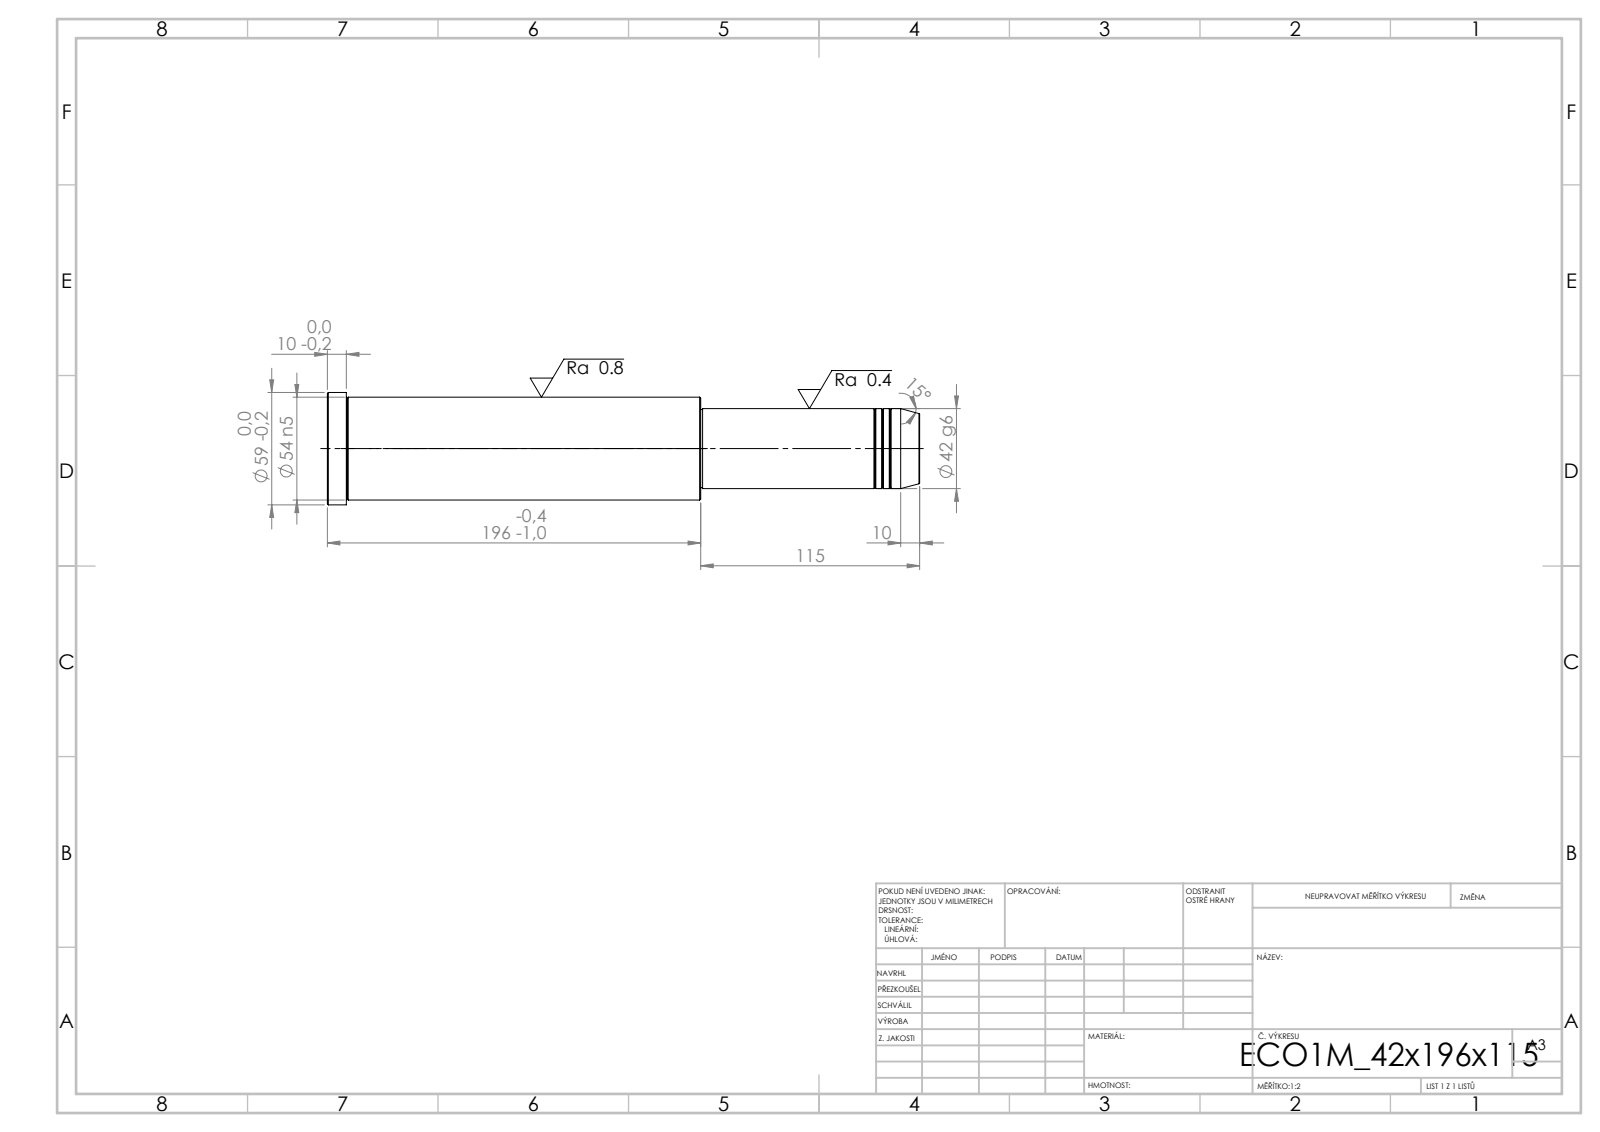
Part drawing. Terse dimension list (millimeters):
written by: SolidWorks 2019 (CONFIG_CONTROL_DESIGN)
unit: mm
bodies: 1 solid, 43 faces (5 planar, 14 cylindrical, 24 other)
size: 311 × 59 × 59
volume: 610 622 mm³; area: 53 998 mm²
bosses: 1× ⌀59, 1× ⌀54, 1× ⌀42, 1× ⌀41
face distances: 311, 115, 196, 301, 186, 10, 114, 1, 187, 197
